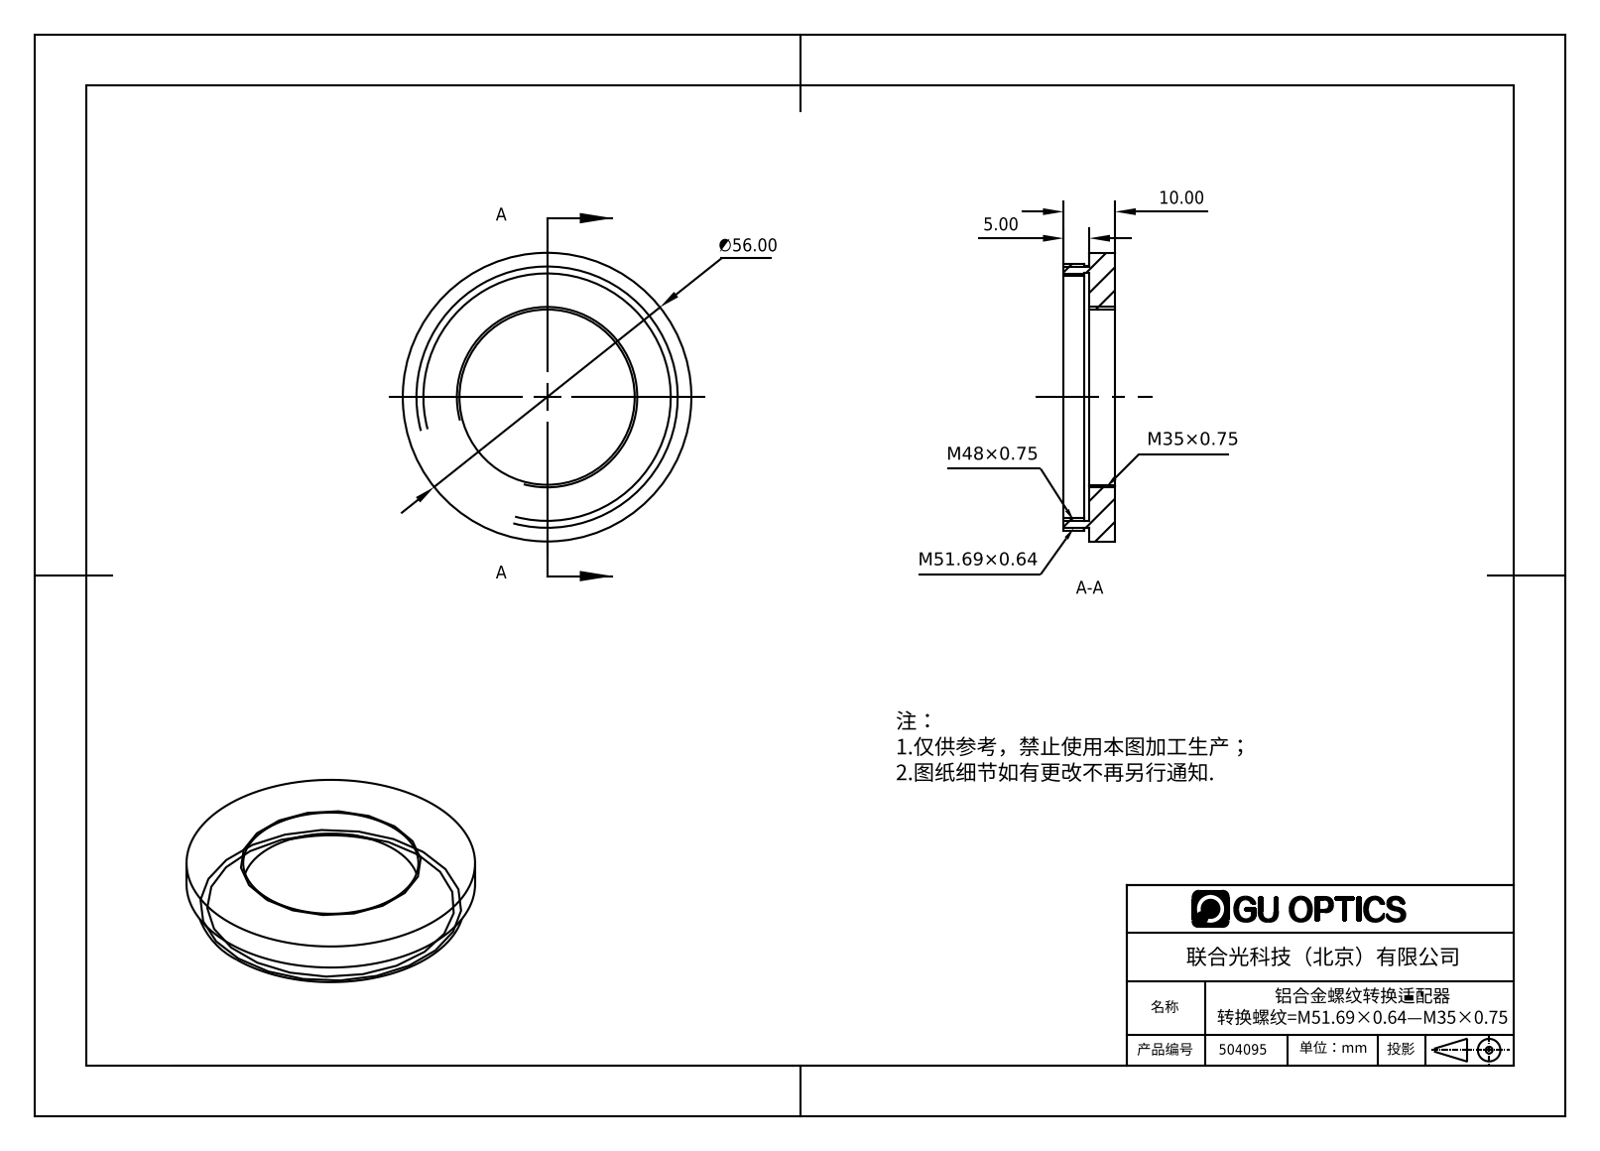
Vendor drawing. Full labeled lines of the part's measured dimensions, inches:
Part name (STEP PRODUCT): 504095
STEP written by: SolidWorks 2016 (AUTOMOTIVE_DESIGN)
Units: inches
Bodies: 1 solid, 18 faces (6 planar, 12 cylindrical, 0 other)
Overall size (bounding box): 2.205 × 2.205 × 0.394
Volume: 0.576 in³ · Surface area: 9.892 in²
Round holes (diameter × count): ⌀1.339 ×1, ⌀1.85 ×1, ⌀1.898 ×1
Round bosses / shafts (diameter × count): ⌀2.205 ×1, ⌀2.035 ×1, ⌀2.004 ×1
Main face-to-face distances: 0.197, 0.394, 0.157, 0.039, 0.236
